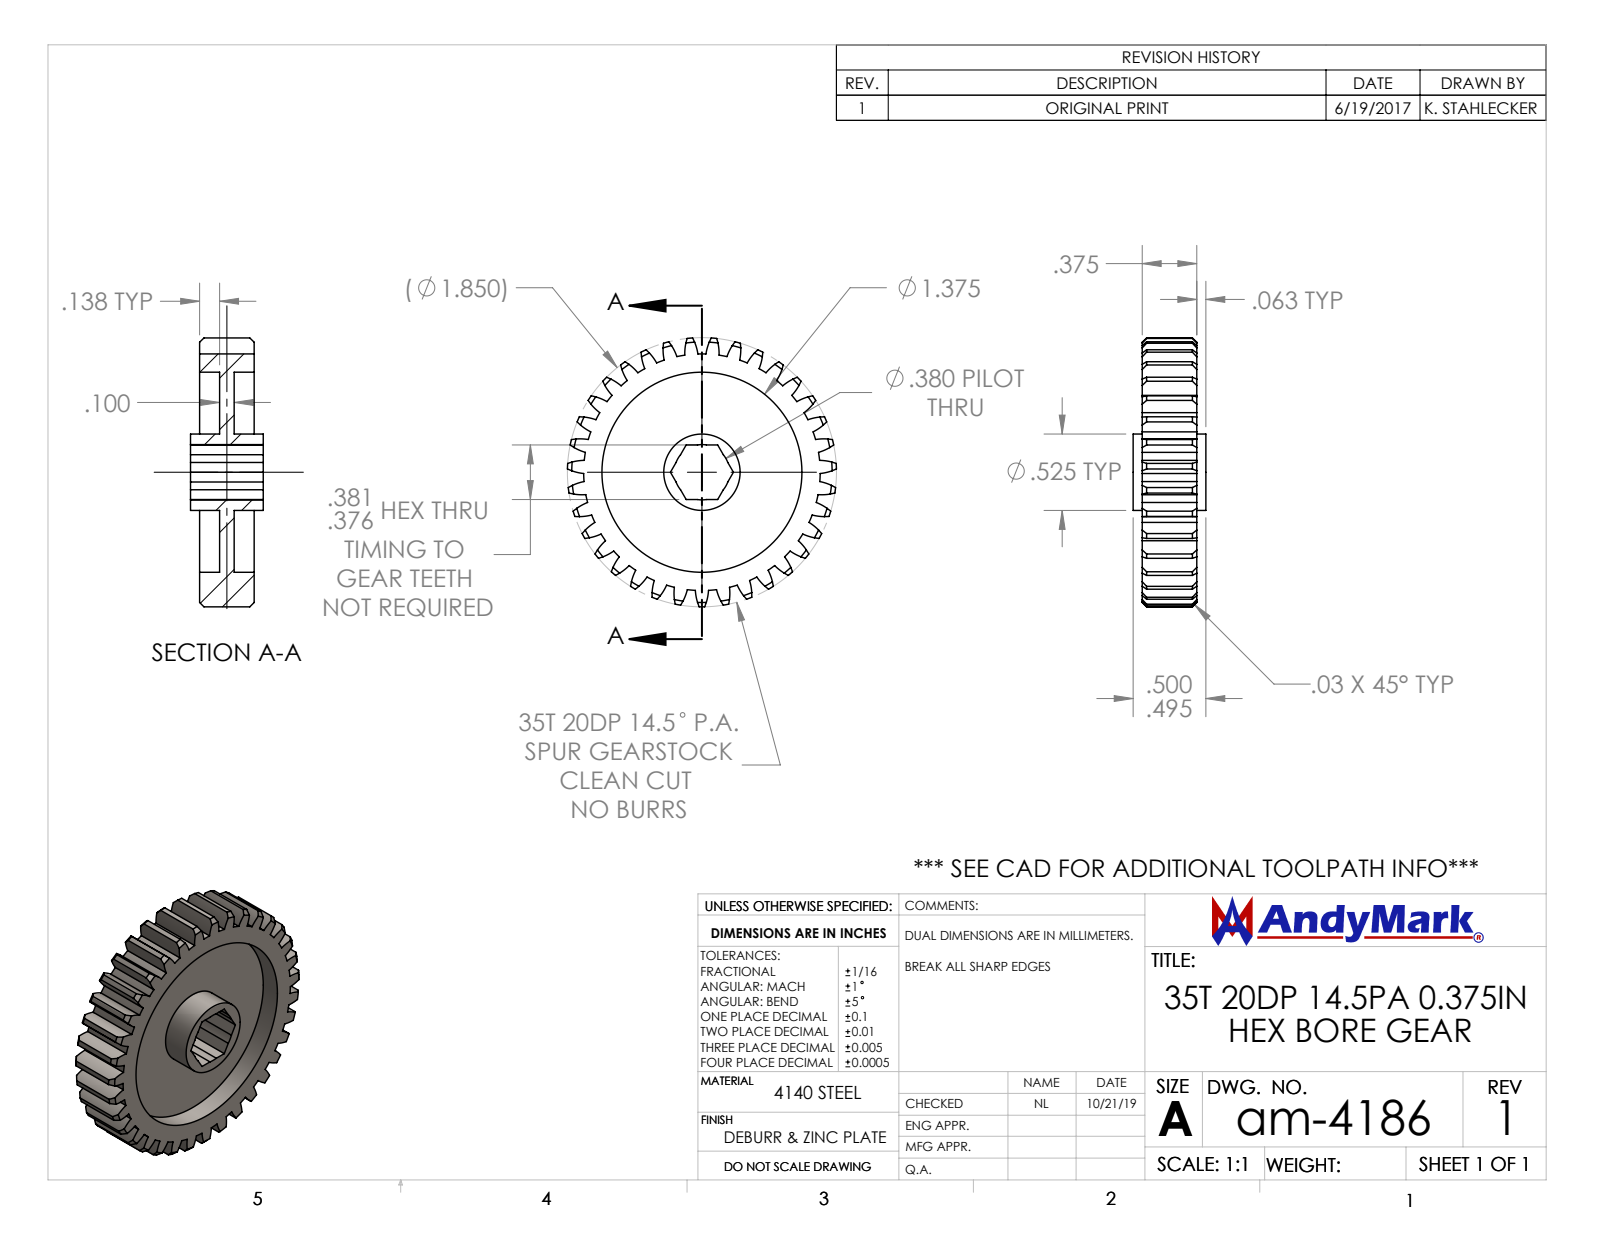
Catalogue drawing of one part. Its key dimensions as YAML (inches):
part_name: "am-4186 35T 20DP 375hex 375 FW"
step_written_by: "SolidWorks 2019 (CONFIG_CONTROL_DESIGN)"
units: inches
bodies: {solids: 1, faces: 246, planar: 18, cylindrical: 158, other: 70}
overall_size: [1.849, 1.848, 0.5]
volume: 0.499
surface_area: 11.15
round_holes:
  - {diameter: 1.375, count: 1}
round_bosses_or_shafts:
  - {diameter: 0.525, count: 1}
partial_cylinders:
  - {radius: 0.35, count: 70}
  - {radius: 0.19, count: 1}
  - {radius: 0.813, count: 1}
  - {radius: 0.925, count: 1}
face_to_face_distances: [0.1, 0.137, 0.237, 0.375, 0.238, 0.138, 0.375, 0.2, 0.3, 0.063]
